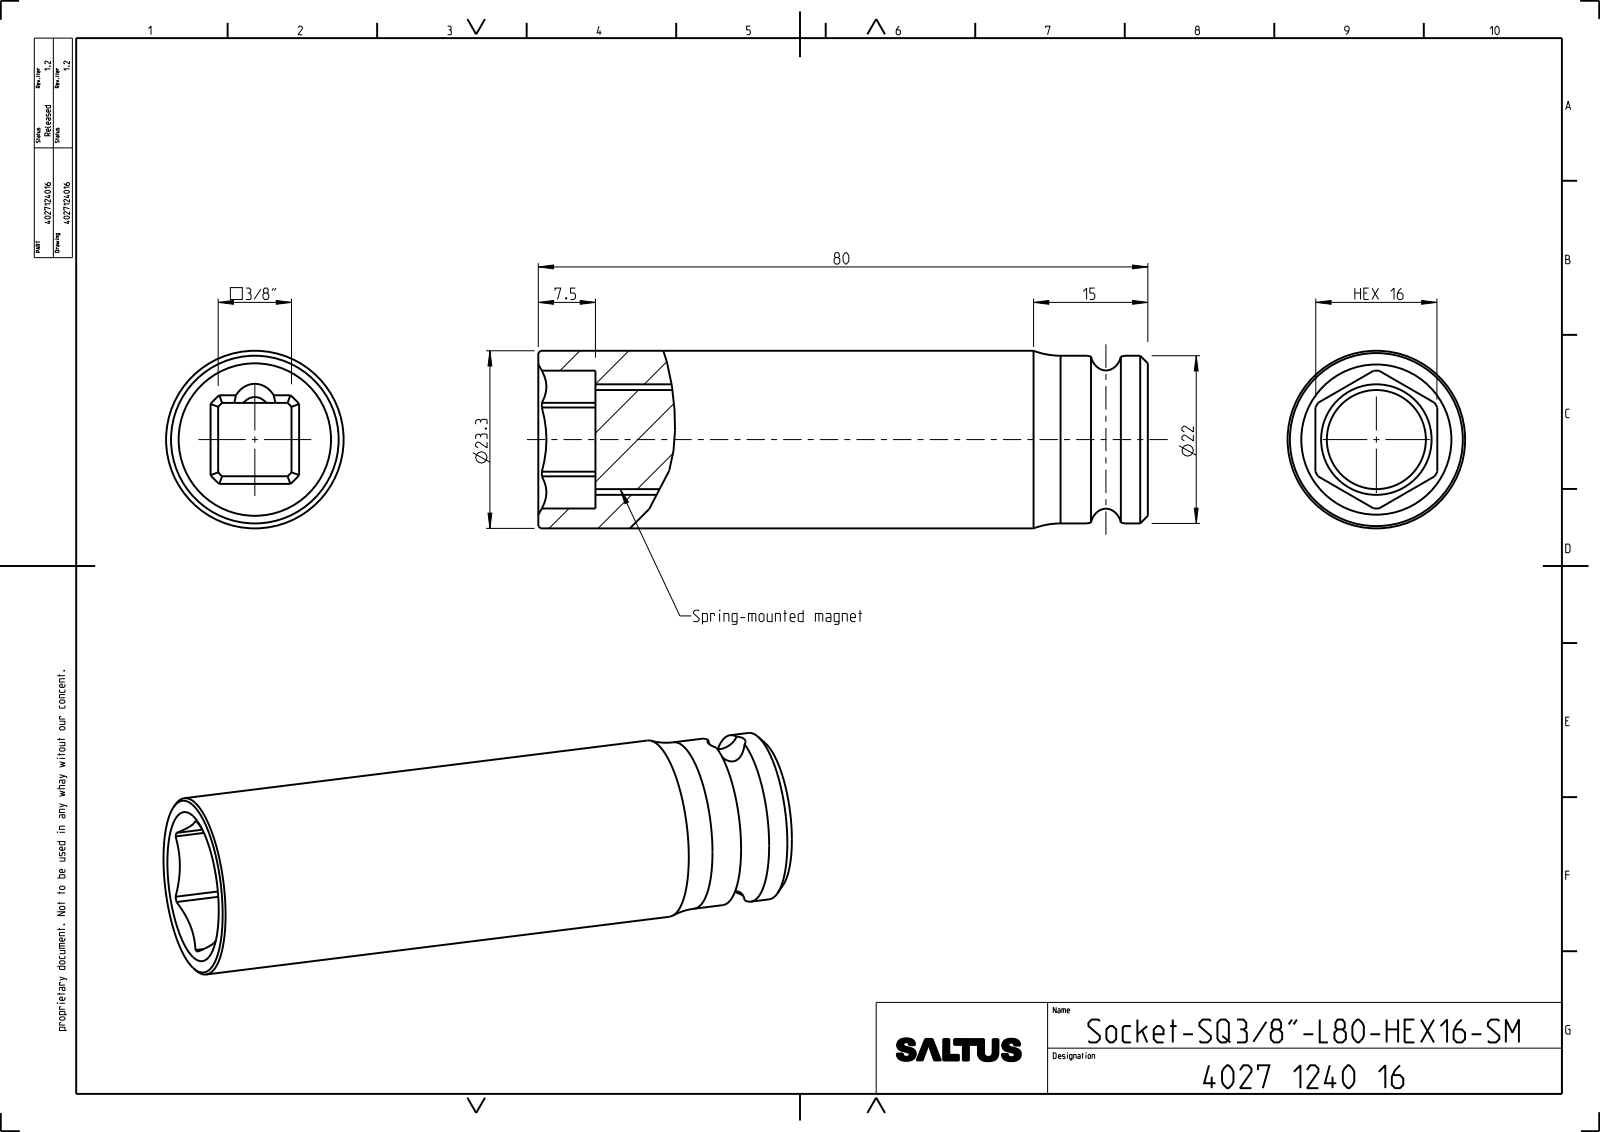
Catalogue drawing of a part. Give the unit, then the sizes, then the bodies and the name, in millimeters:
Units: millimetres
Overall size (bounding box): 80 × 23.3 × 23.3
Round holes (diameter × count): ⌀5 ×1, ⌀14.5 ×1
Round bosses / shafts (diameter × count): ⌀23.3 ×1, ⌀22 ×1, ⌀13 ×1
Partial cylindrical surfaces — rounded edges, fillets, slot ends (radius × count): R3 ×1, R6.45 ×1, R9.04 ×1
Main face-to-face distances: 72.5, 16, 9.62, 57.5, 15, 3.19, 12.81, 80, 22.5, 7.5
Volume: 22 047 mm³ · Surface area: 10 942 mm²
Bodies: 2 solids, 61 faces (20 planar, 25 cylindrical, 16 other)
Part name (STEP PRODUCT): 4027124016
STEP written by: CREO PARAMETRIC BY PTC INC, 2022414 (CONFIG_CONTROL_DESIGN)
